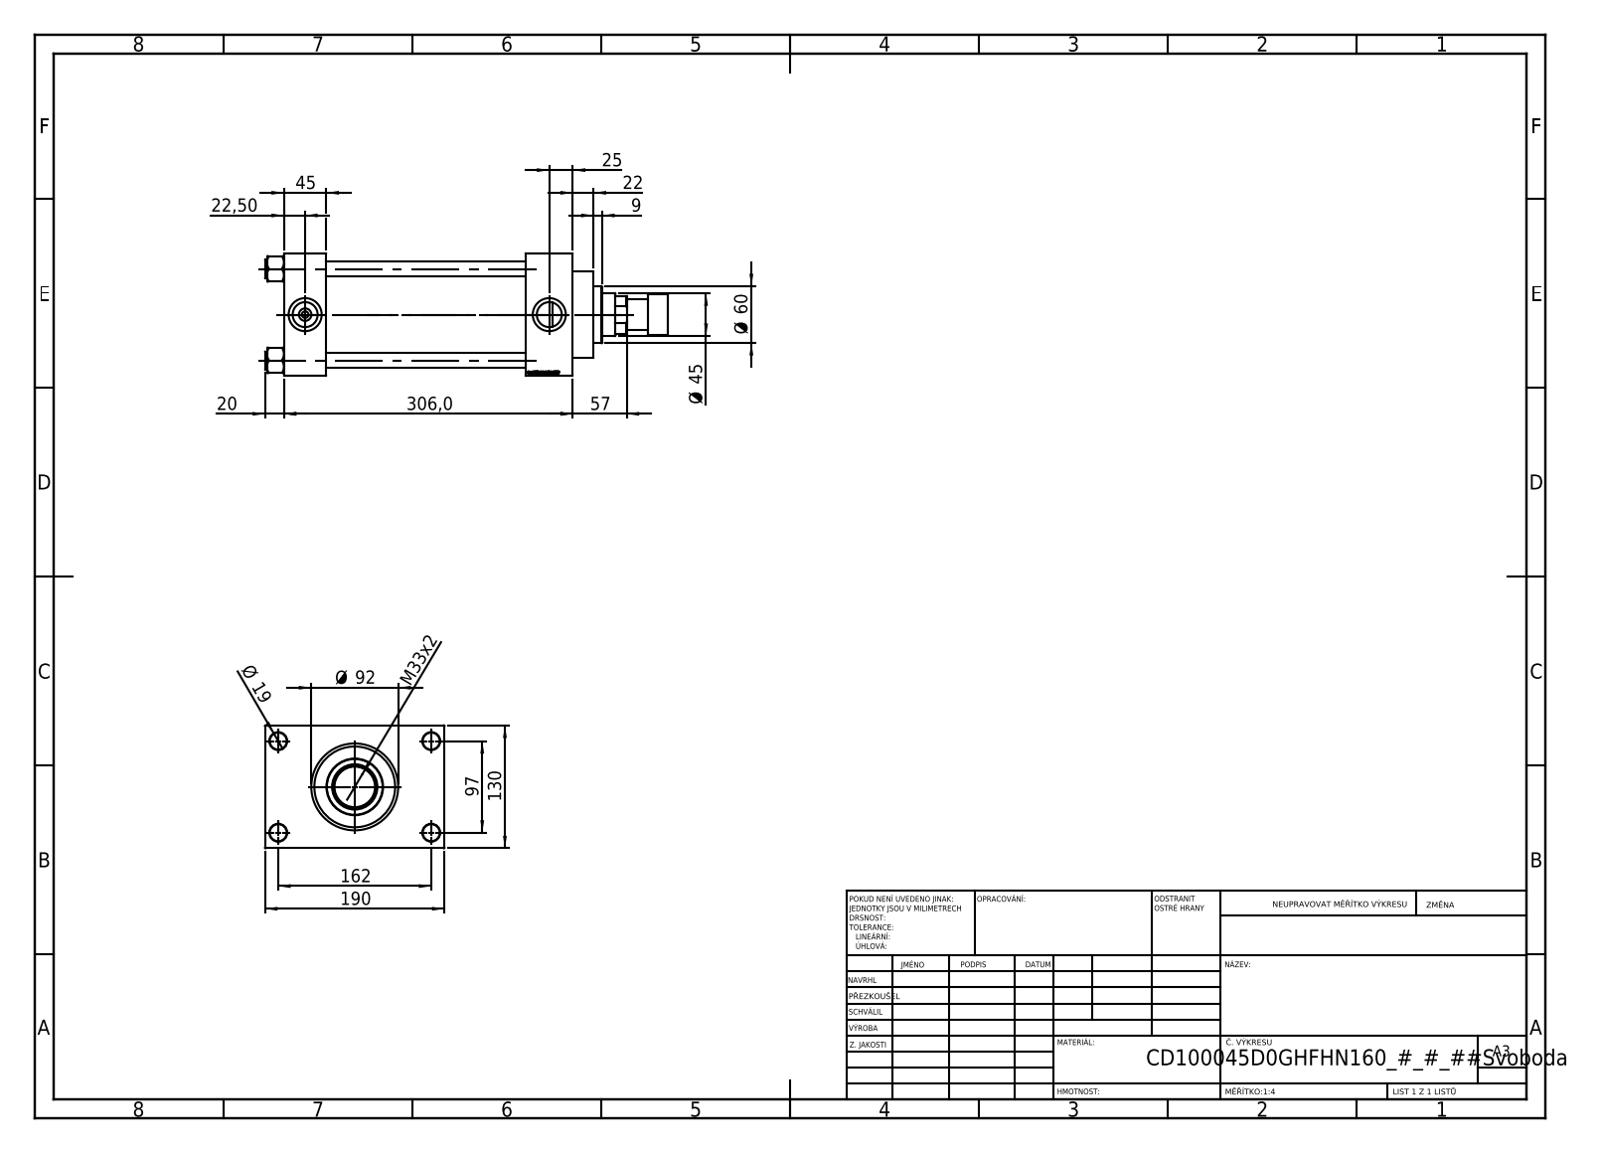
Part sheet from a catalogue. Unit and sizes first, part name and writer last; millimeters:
Units: millimetres
Overall size (bounding box): 427 × 190 × 130
Round holes (diameter × count): ⌀16 ×4, ⌀18 ×4, ⌀7 ×2, ⌀26.44 ×2, ⌀35 ×2, ⌀31.5 ×1, ⌀45 ×1, ⌀48 ×1, ⌀76 ×1, ⌀85.5 ×1, ⌀100 ×1
Round bosses / shafts (diameter × count): ⌀19 ×4, ⌀106 ×1, ⌀92 ×1, ⌀60 ×1, ⌀44 ×1, ⌀33 ×1
Main face-to-face distances: 130, 45, 256, 211, 306, 261, 50, 160, 30, 96
Hole centre spacings: 32.55, 68.52, 94.41, 96.9, 102.27, 129.45, 161.73, 97
Volume: 3 114 000 mm³ · Surface area: 501 800 mm²
Bodies: 12 solids, 1164 faces (548 planar, 92 cylindrical, 524 other)
Part name (STEP PRODUCT): V215CD_VCP_D; V215CR_ROD_END_F; V215CD_VC_A; V215CD_D_TYCINKA (+2 more)
STEP written by: SolidWorks 2019 (CONFIG_CONTROL_DESIGN)
